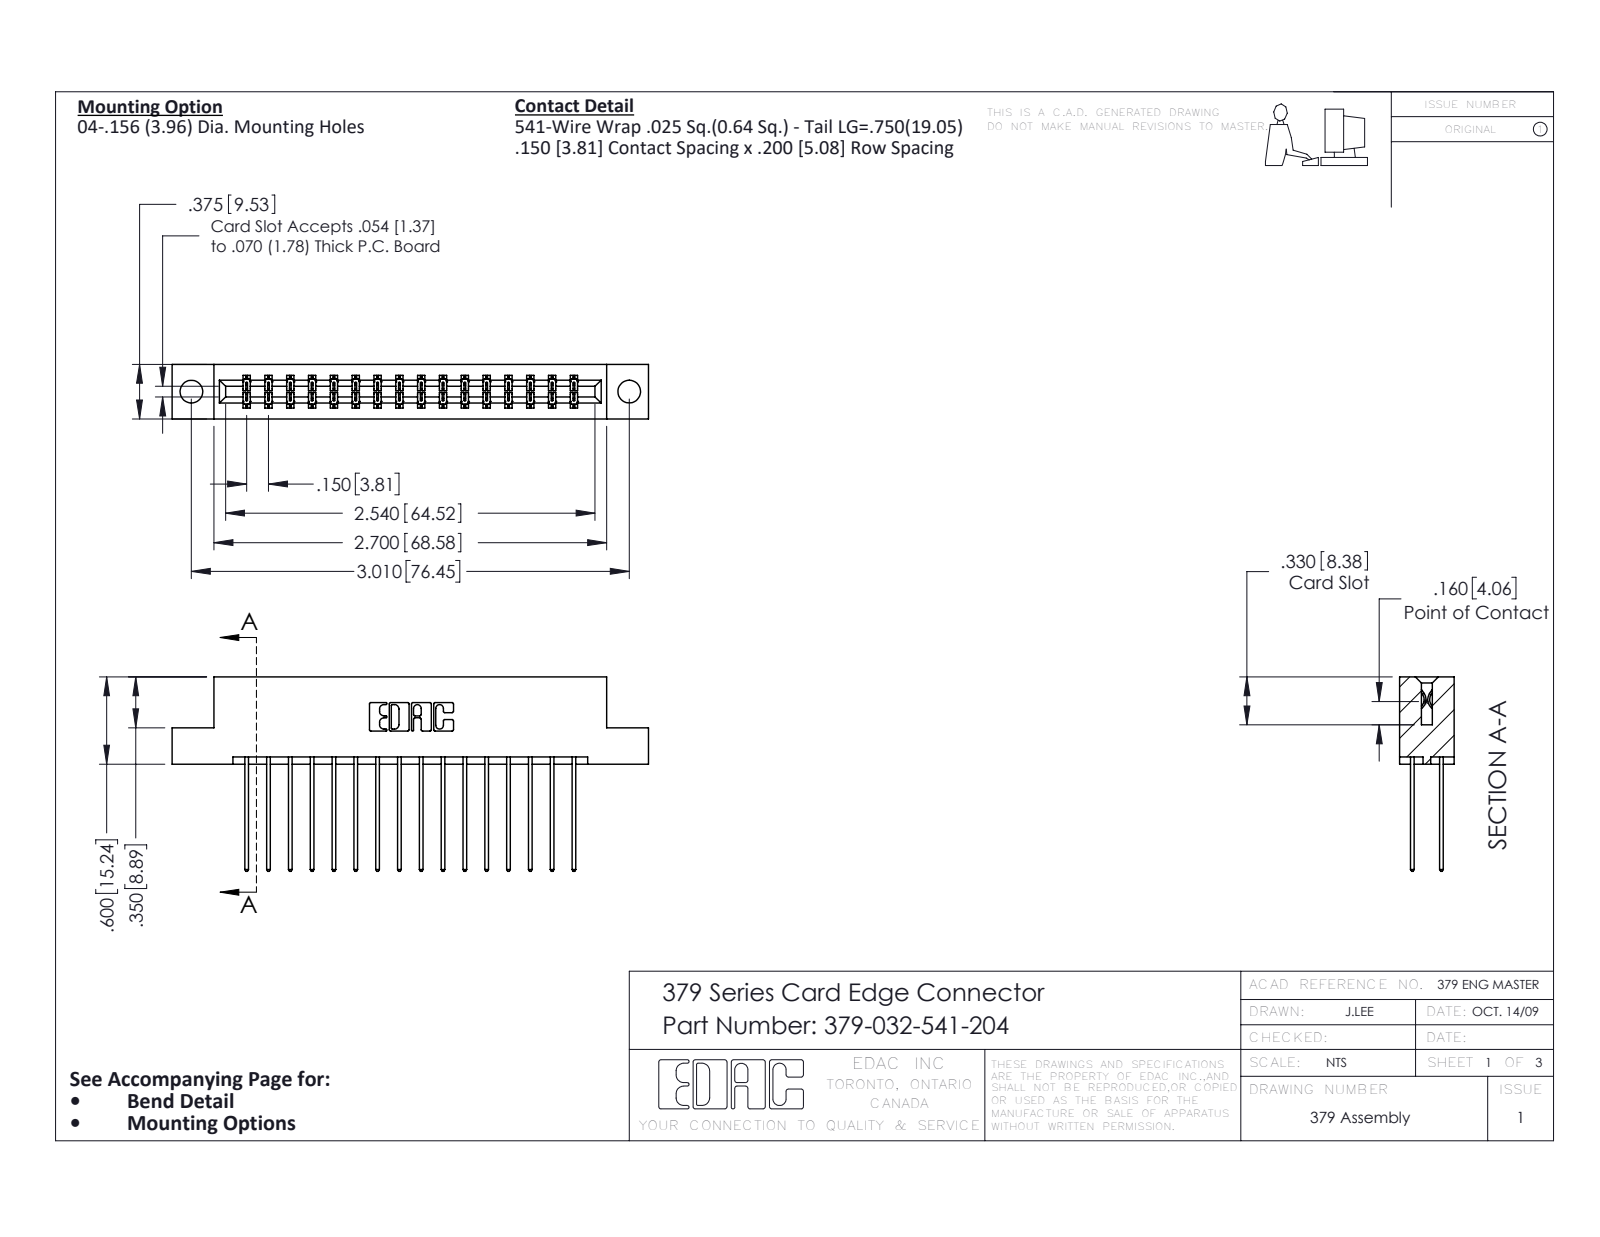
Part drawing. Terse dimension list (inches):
name: 345-292-001_345-293-141; 379 Part_Flush - .156 Dia - TH; 379-032-541-204
written by: SolidWorks 2020 (CONFIG_CONTROL_DESIGN)
unit: in
bodies: 33 solids, 1778 faces (1222 planar, 556 cylindrical, 0 other)
size: 3.275 × 1.337 × 0.375
volume: 0.527 in³; area: 15.77 in²
holes: 2× ⌀0.156
rounds: 63× R0.006, 32× R0.01, 22× R0.01, 6× R0.007, 6× R0.031, 3× R0.026, 2× R0.014, 2× R0.022
face distances: 0.3, 0.075, 0.2, 0.1, 0.375, 0.275, 0.15, 0.025, 0.05, 0.6
hole spacings: 3.01
